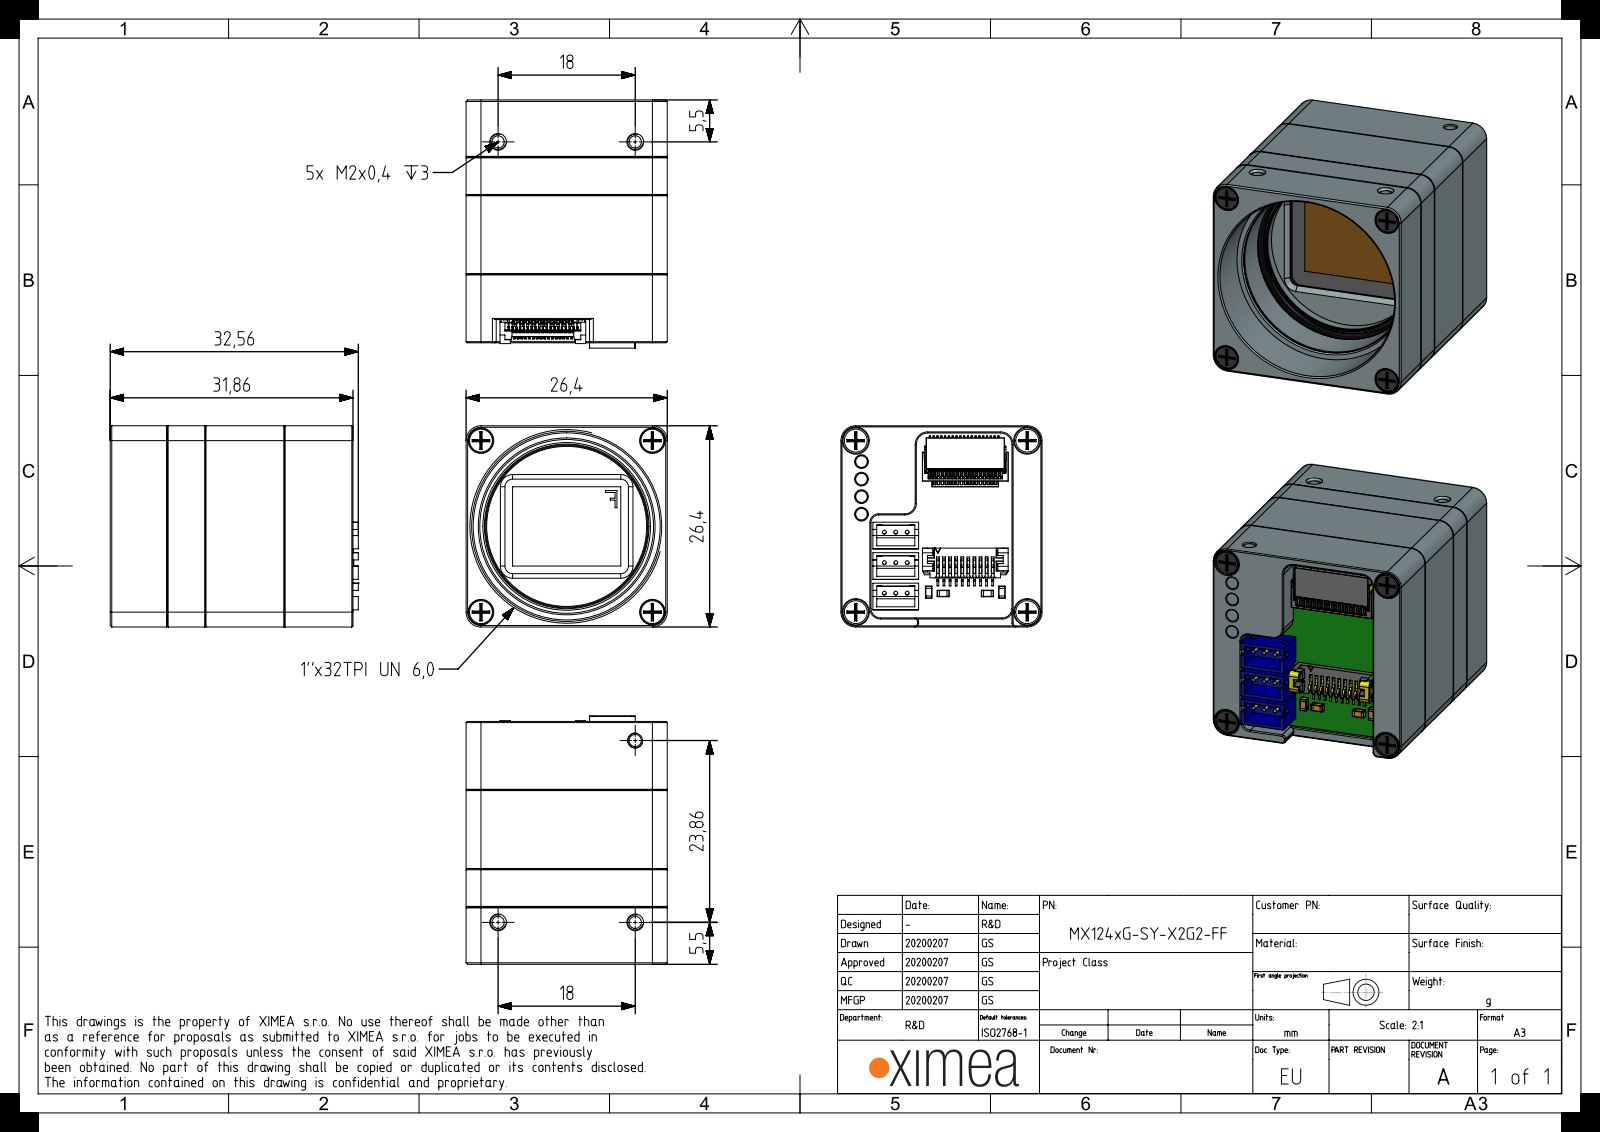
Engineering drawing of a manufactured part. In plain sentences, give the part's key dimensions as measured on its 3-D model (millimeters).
The part is named "MT124xG-PR-SENSOR-PCA; MECH-O-RING-22X1-VI370; FLT-BK7-AR2X-D25; SROB-M1.6x3-SLOT-STNLS (+8 more)". Its 3-D file was written by "SIEMENS PLM Software NX 1907 (AUTOMOTIVE_DESIGN)". It is 305 solids with 20262 faces: 11968 planar, 5735 cylindrical and 2559 other. Overall it measures 32.6 by 26.4 by 26.4 millimeters. Its volume is 11 500 cubic millimeters and its surface area 23 300 square millimeters. Round holes: 15 of diameter 1.6, 9 of diameter 0.7, 8 of diameter 2, 4 of diameter 0.9, 4 of diameter 0.9, 4 of diameter 2.1, 4 of diameter 3, 4 of diameter 3.2, 4 of diameter 3.4, 3 of diameter 0.3, 2 of diameter 0.6, 2 of diameter 0.8. Round bosses or shafts: 9 of diameter 0.5, 8 of diameter 1.9, 6 of diameter 3, 4 of diameter 1.6, 4 of diameter 0.8, 2 of diameter 1.6, 2 of diameter 0.8, 1 of diameter 25. Partial cylindrical surfaces (rounded edges, fillets, slot ends): 77 of radius 0.1, 74 of radius 0.1, 30 of radius 0.2, 30 of radius 0.3, 27 of radius 0.4, 18 of radius 1, 18 of radius 1.5, 15 of radius 0.2. The main face-to-face distances are 1, 3.6, 26.4, 4.6, 6.9, 11.5, 10.5, 2.5, 5.7, 4.2. The hole center spacings are 4.3, 1.5, 4, 5, 8.1, 22.5, 2.3, 3.
